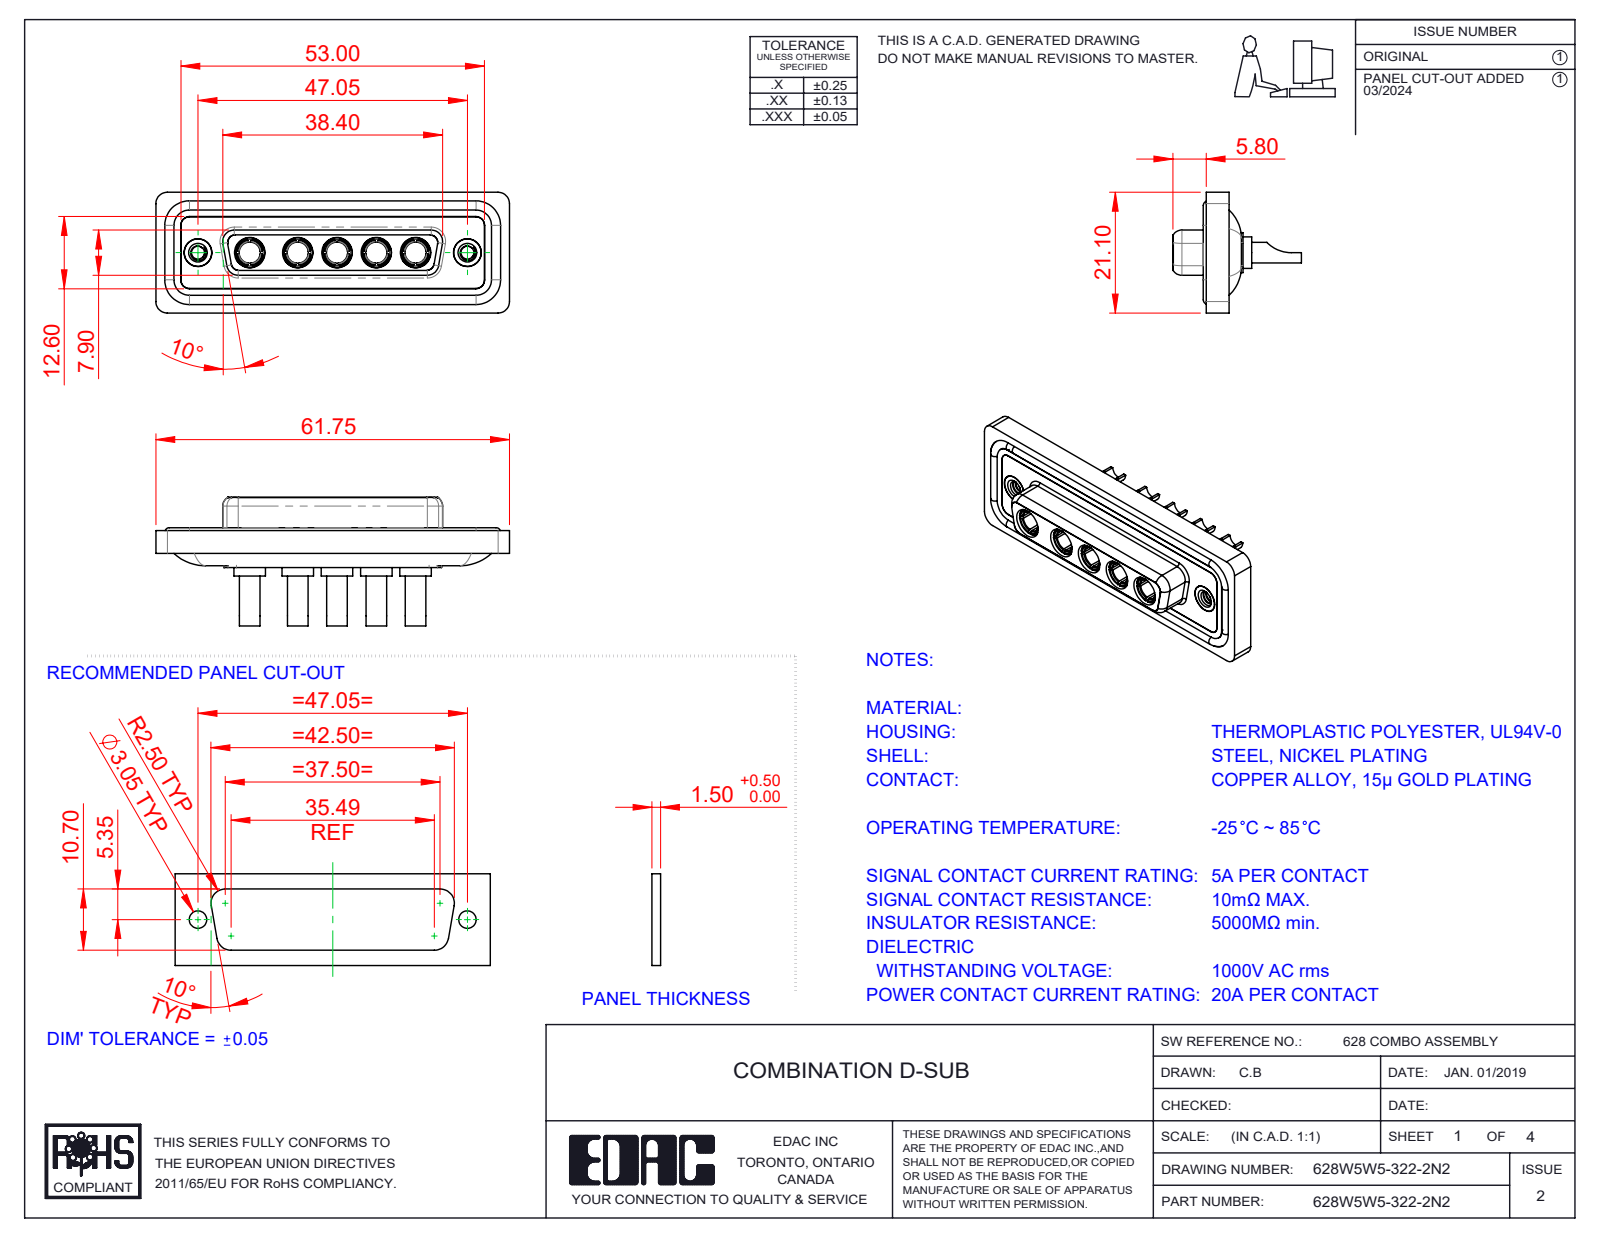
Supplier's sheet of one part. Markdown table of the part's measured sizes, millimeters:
| quantity | value |
| --- | --- |
| part name | 628Combo Shell Front_25 Contacts; 628Combo Shell Rear_25 Contacts; 628Combo Waterproof Housing_25 Contacts; Power Socket_20A SC (+3 more) |
| STEP written by | SolidWorks 2020 (CONFIG_CONTROL_DESIGN) |
| units | millimeters |
| bodies | 17 solids, 791 faces (265 planar, 318 cylindrical, 208 other) |
| overall size | 61.75 × 22.45 × 21.1 |
| volume | 8 237 mm³ |
| surface area | 13 828 mm² |
| round holes (diameter × count) | 4.85 × 7, 2.7 × 5, 3.7 × 5, 5.3 × 5, 2.26 × 2, 4 × 2, 4.05 × 2, 5 × 2 |
| round bosses / shafts (diameter × count) | 5.5 × 5, 5.2 × 5, 4.96 × 5, 4.75 × 5, 3.75 × 5, 3.6 × 5, 1.6 × 4, 4.95 × 2 |
| partial cylindrical surfaces (radius × count) | 1.5 × 22, 2 × 18, 1.35 × 8, 1.6 × 8, 2.1 × 5, 0.25 × 4, 0.5 × 4, 0.6 × 4 |
| main face-to-face distances | 0.4, 1.8, 7.45, 5.65, 0.5, 7.05, 6.6, 1.6, 1.1, 2.9 |
| hole center spacings | 6.86, 9.04, 13.72, 38.01, 8.39, 15.25, 15.9, 17.43 |
